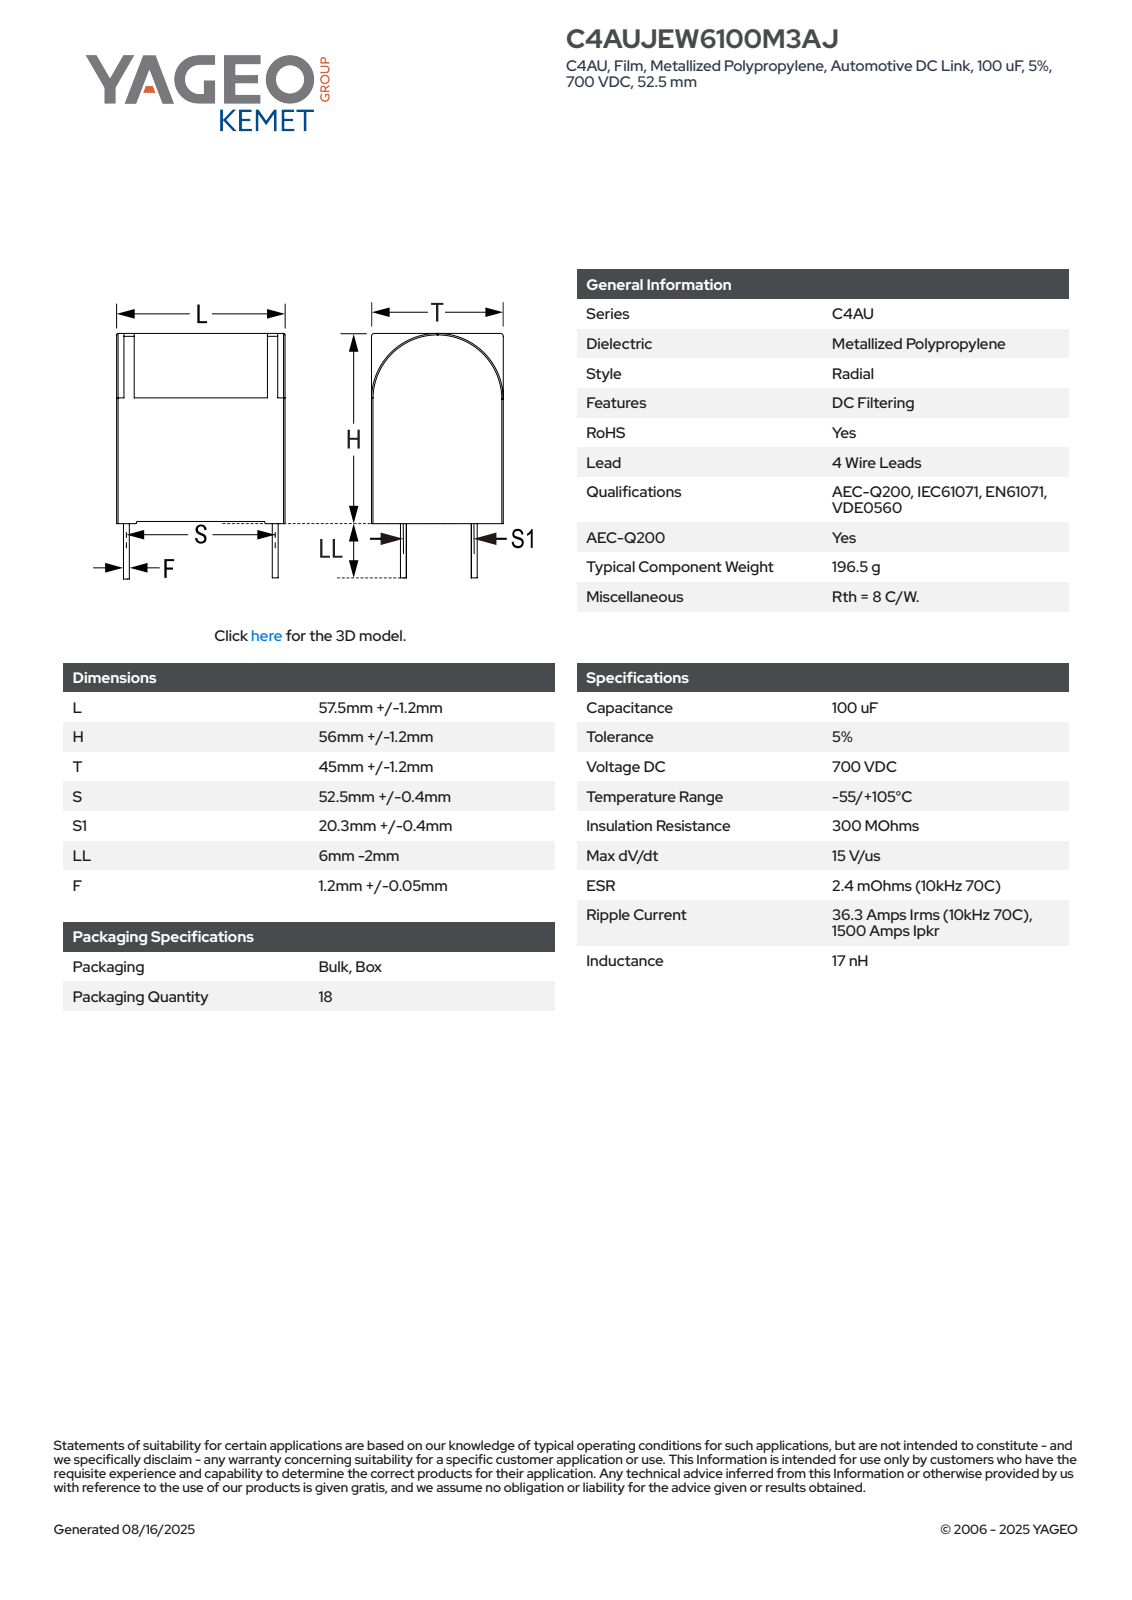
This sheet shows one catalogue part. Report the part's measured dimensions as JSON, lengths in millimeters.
{"part_name": "CFP_RB4_57.5X56X45_L58.7H57.2T46.2S52.5S120.3LL4F1.25", "step_written_by": "SolidWorks 2021 (AUTOMOTIVE_DESIGN)", "units": "millimeters", "bodies": {"solids": 4, "faces": 103, "planar": 92, "cylindrical": 11, "other": 0}, "overall_size": [61.2, 58.7, 46.2], "volume_mm3": 141280, "surface_area_mm2": 17362, "round_bosses_or_shafts": [[1.25, 4]], "partial_cylinders_radius": [[23.1, 1]], "face_to_face_distances": [58.7, 46.2, 55.52, 3.5, 55.2, 11.35, 47.35, 7.85, 43.85, 1.68]}
